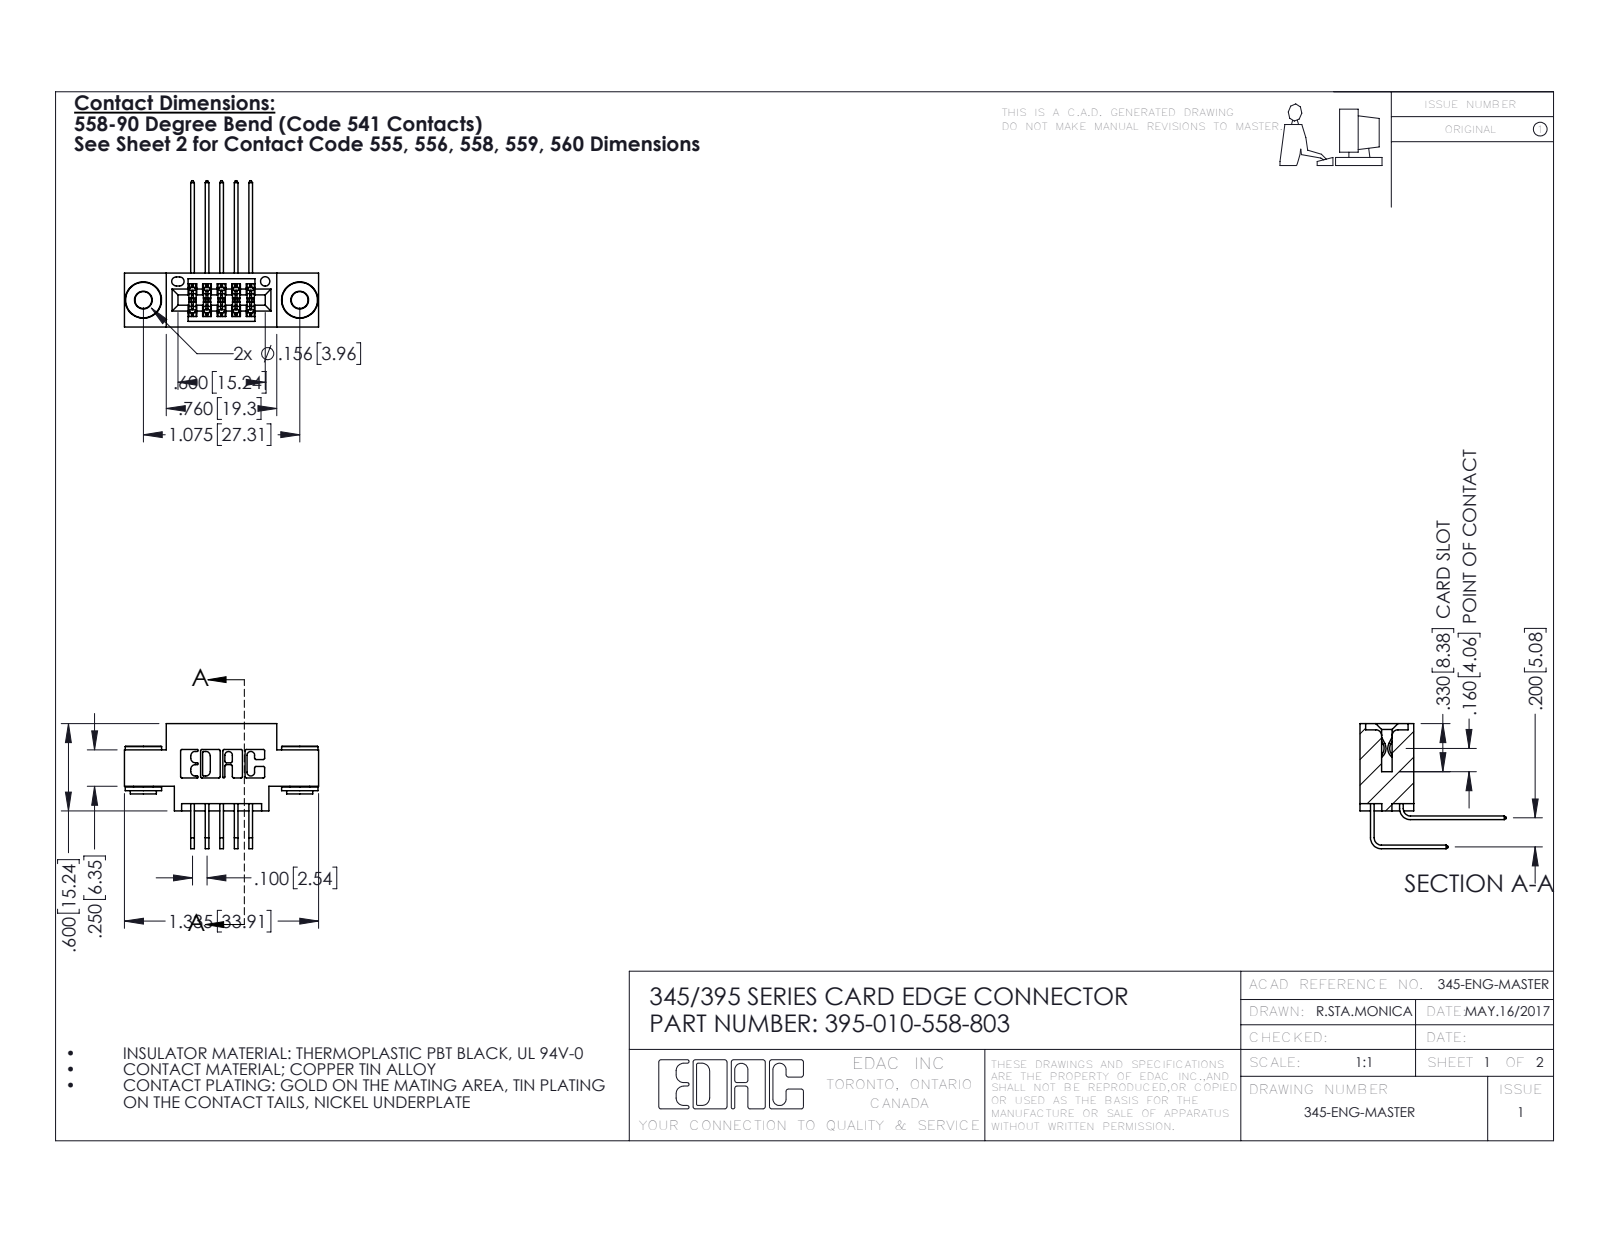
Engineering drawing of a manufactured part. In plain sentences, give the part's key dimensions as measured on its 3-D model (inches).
The part is named "395-010-558-803; 345 Part_0.170 Offset - 0.156 Dia-TH; 345-250-002_345-250-002-102; 345-292-001_558 Tail - 2 (+1 more)". Its 3-D file was written by "SolidWorks 2016 (CONFIG_CONTROL_DESIGN)". It is 13 solids with 688 faces: 444 planar, 236 cylindrical and 8 other. Overall it measures 1.335 by 1.005 by 0.859 inches. Its volume is 0.178 cubic inches and its surface area 6.527 square inches. Round holes: 2 of diameter 0.116, 2 of diameter 0.156, 1 of diameter 0.064. Round bosses or shafts: 2 of diameter 0.25, 2 of diameter 0.18, 2 of diameter 0.136. Partial cylindrical surfaces (rounded edges, fillets, slot ends): 22 of radius 0.01, 16 of radius 0.006, 6 of radius 0.007, 6 of radius 0.031, 3 of radius 0.026, 2 of radius 0.014, 2 of radius 0.019, 2 of radius 0.022. The main face-to-face distances are 0.2, 0.37, 0.1, 0.072, 0.298, 0.25, 0.098, 0.272, 0.025, 0.025. The hole center spacings are 0.27, 0.847, 1.075.
